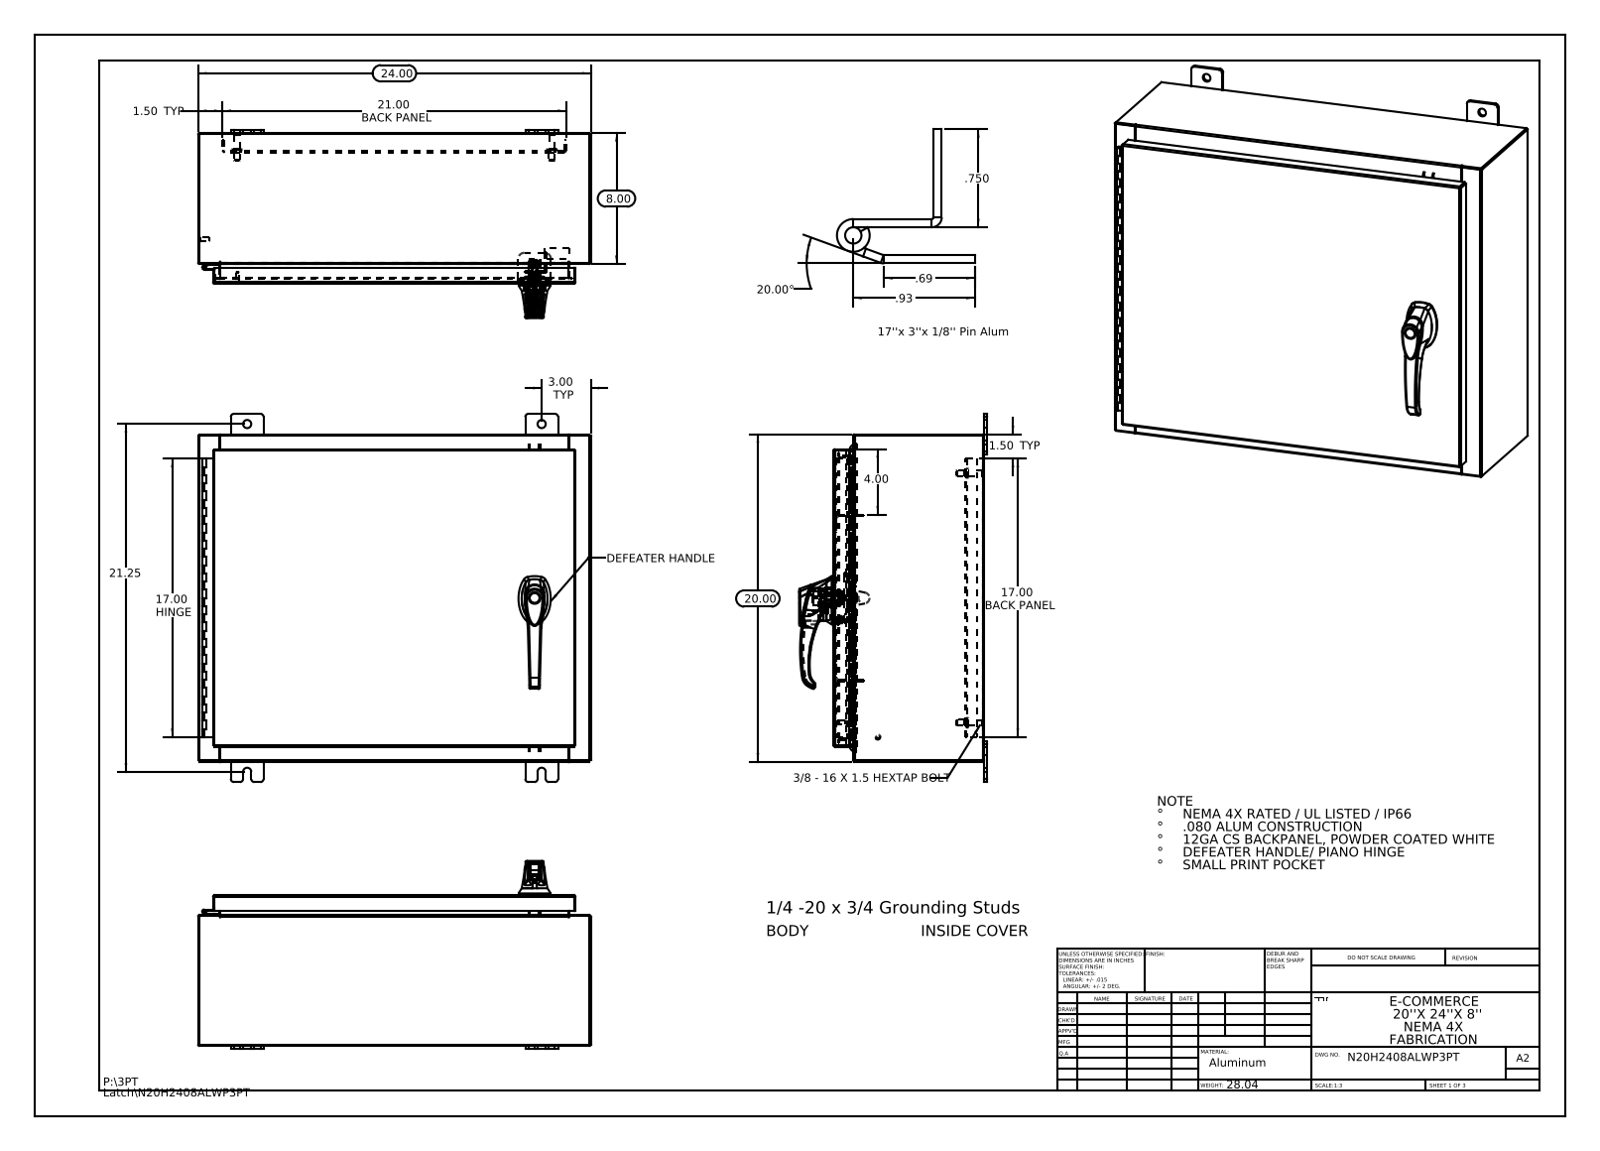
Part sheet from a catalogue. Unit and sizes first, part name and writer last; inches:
Units: inches
Overall size (bounding box): 24 × 22.5 × 11.495
Round holes (diameter × count): ⌀0.5 ×8, ⌀0.25 ×4, ⌀0.138 ×3, ⌀0.161 ×3, ⌀0.079 ×2, ⌀0.203 ×2, ⌀0.313 ×2, ⌀0.437 ×2, ⌀0.125 ×1, ⌀0.125 ×1, ⌀0.197 ×1, ⌀0.276 ×1
Round bosses / shafts (diameter × count): ⌀0.625 ×4, ⌀0.375 ×4, ⌀0.33 ×4, ⌀0.157 ×4, ⌀0.14 ×4, ⌀0.315 ×3, ⌀0.236 ×3, ⌀1.181 ×1
Partial cylindrical surfaces — rounded edges, fillets, slot ends (radius × count): R0.118 ×37, R0.006 ×33, R0.19 ×24, R0.013 ×22, R0.088 ×18, R0.039 ×15, R0.028 ×12, R0.008 ×6
Main face-to-face distances: 0.075, 9.126, 9.051, 9.201, 0.104, 19.925, 1, 1.075, 8.051, 8.126
Hole centre spacings: 3.404, 0.295, 0.625, 0.841, 1.25, 1.313, 1.561, 1.858
Volume: 192.7 in³ · Surface area: 4 762 in²
Bodies: 37 solids, 2402 faces (835 planar, 869 cylindrical, 698 other)
Part name (STEP PRODUCT): N20H2408ALWP3PT Mounting Studs; Quarter-20 CD Stud; N20H2408ALWP3PT; 012103_012102 (+8 more)
STEP written by: SolidWorks 2013 (CONFIG_CONTROL_DESIGN)
